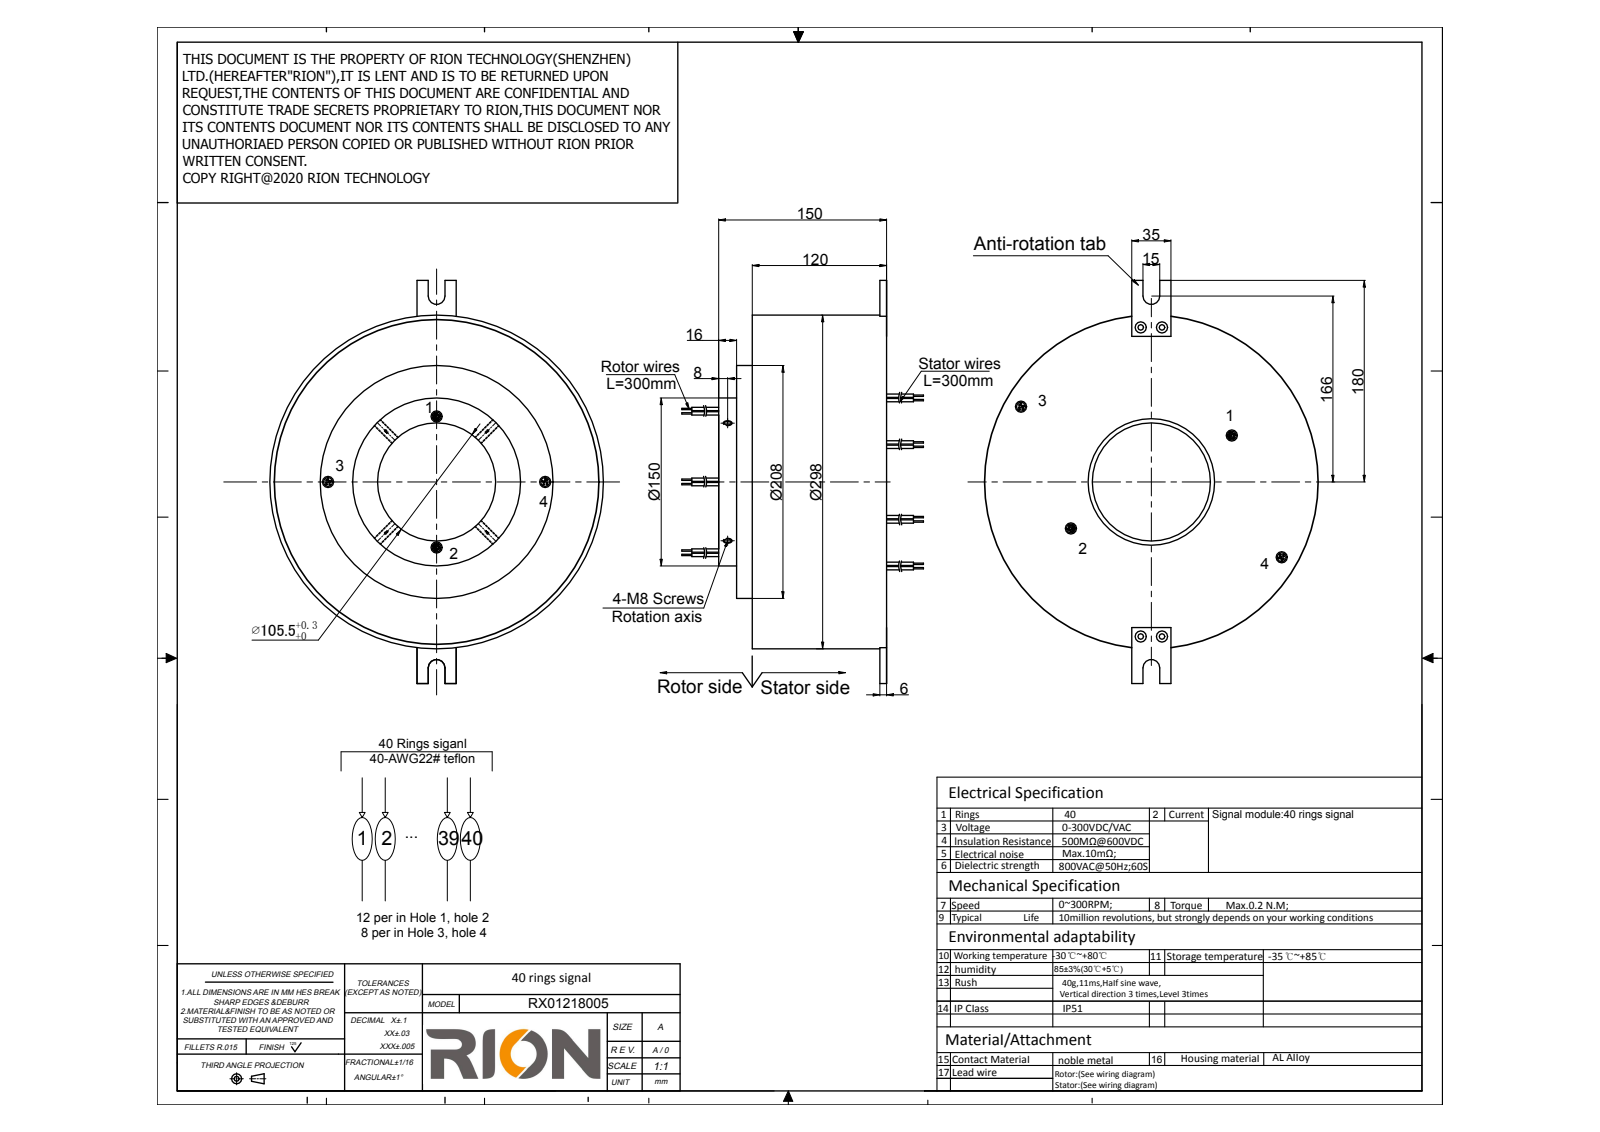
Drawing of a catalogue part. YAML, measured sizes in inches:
part_name: "RX01218005"
step_written_by: "SolidWorks 2014 (CONFIG_CONTROL_DESIGN)"
units: inches
bodies: {solids: 3, faces: 334, planar: 118, cylindrical: 208, other: 8}
overall_size: [14.173, 11.732, 7.402]
volume: 477.4
surface_area: 494.1
round_holes:
  - {diameter: 0.315, count: 8}
  - {diameter: 0.197, count: 4}
  - {diameter: 0.276, count: 4}
  - {diameter: 4.154, count: 1}
round_bosses_or_shafts:
  - {diameter: 0.051, count: 80}
  - {diameter: 11.732, count: 1}
  - {diameter: 8.189, count: 1}
  - {diameter: 5.906, count: 1}
partial_cylinders:
  - {radius: 0.059, count: 4}
  - {radius: 0.295, count: 2}
face_to_face_distances: [4.724, 0.551, 5.276, 0.63, 1.181, 5.906, 0.236, 5.669, 5.039, 4.488]
hole_center_spacings: [3.152, 4.46, 5.446, 6.433, 6.863, 7.745, 0.748, 1.91]
